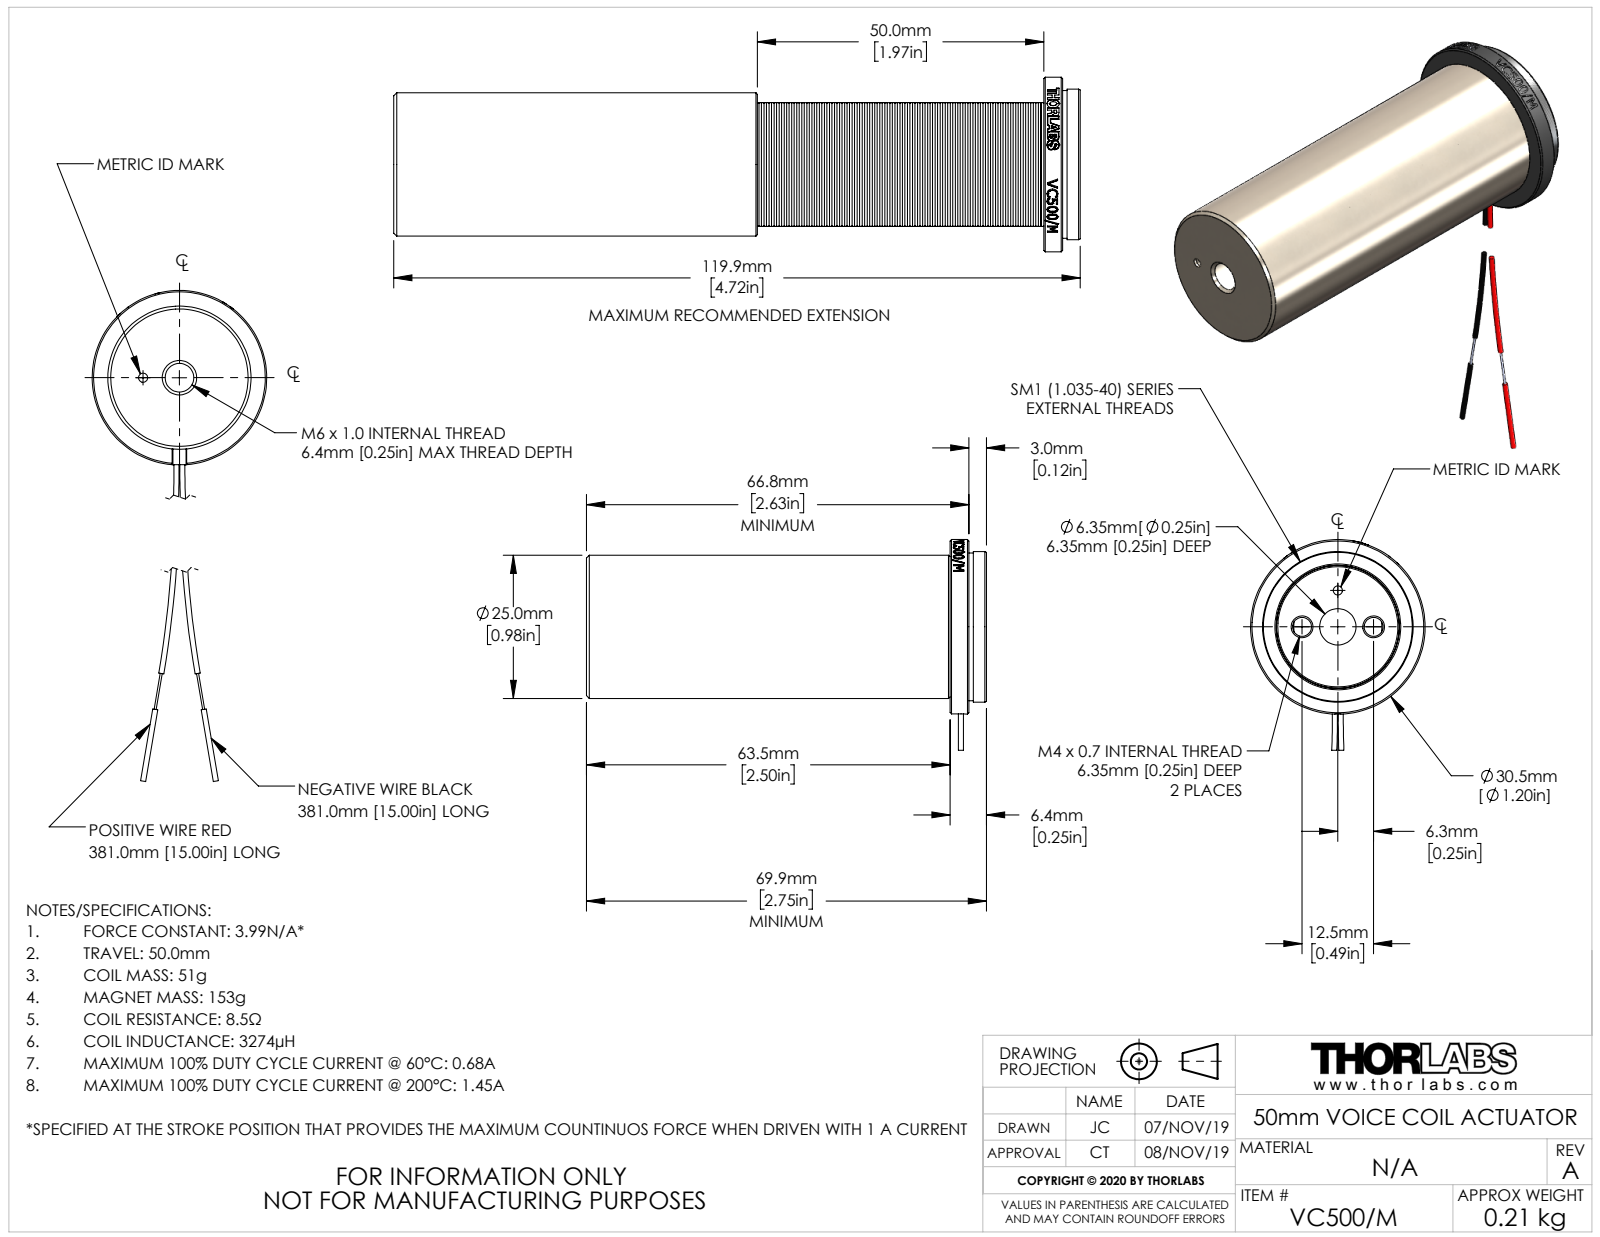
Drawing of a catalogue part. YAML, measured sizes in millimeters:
part_name: "TTN200617-E0W"
step_written_by: "SolidWorks 2018 (AUTOMOTIVE_DESIGN)"
units: millimeters
bodies: {solids: 5, faces: 1129, planar: 105, cylindrical: 322, other: 702}
overall_size: [69.9, 30.5, 30.5]
volume: 31360
surface_area: 24440
round_holes:
  - {diameter: 1.6, count: 2}
  - {diameter: 4, count: 2}
  - {diameter: 6, count: 1}
  - {diameter: 6.4, count: 1}
  - {diameter: 16.7, count: 1}
  - {diameter: 21.4, count: 1}
  - {diameter: 21.6, count: 1}
  - {diameter: 22.4, count: 1}
round_bosses_or_shafts:
  - {diameter: 30.5, count: 1}
  - {diameter: 26.3, count: 1}
  - {diameter: 25.8, count: 1}
  - {diameter: 25, count: 1}
  - {diameter: 21.6, count: 1}
  - {diameter: 21.5, count: 1}
  - {diameter: 21.5, count: 1}
  - {diameter: 17.4, count: 1}
partial_cylinders:
  - {radius: 1.3, count: 1}
  - {radius: 15.2, count: 1}
face_to_face_distances: [6.4, 57.2, 63.5, 69.9, 12.7, 50.8, 3, 3.3, 9.7, 60.5]
hole_center_spacings: [6.2, 6.4, 8.9, 9, 12.5, 12.6]
